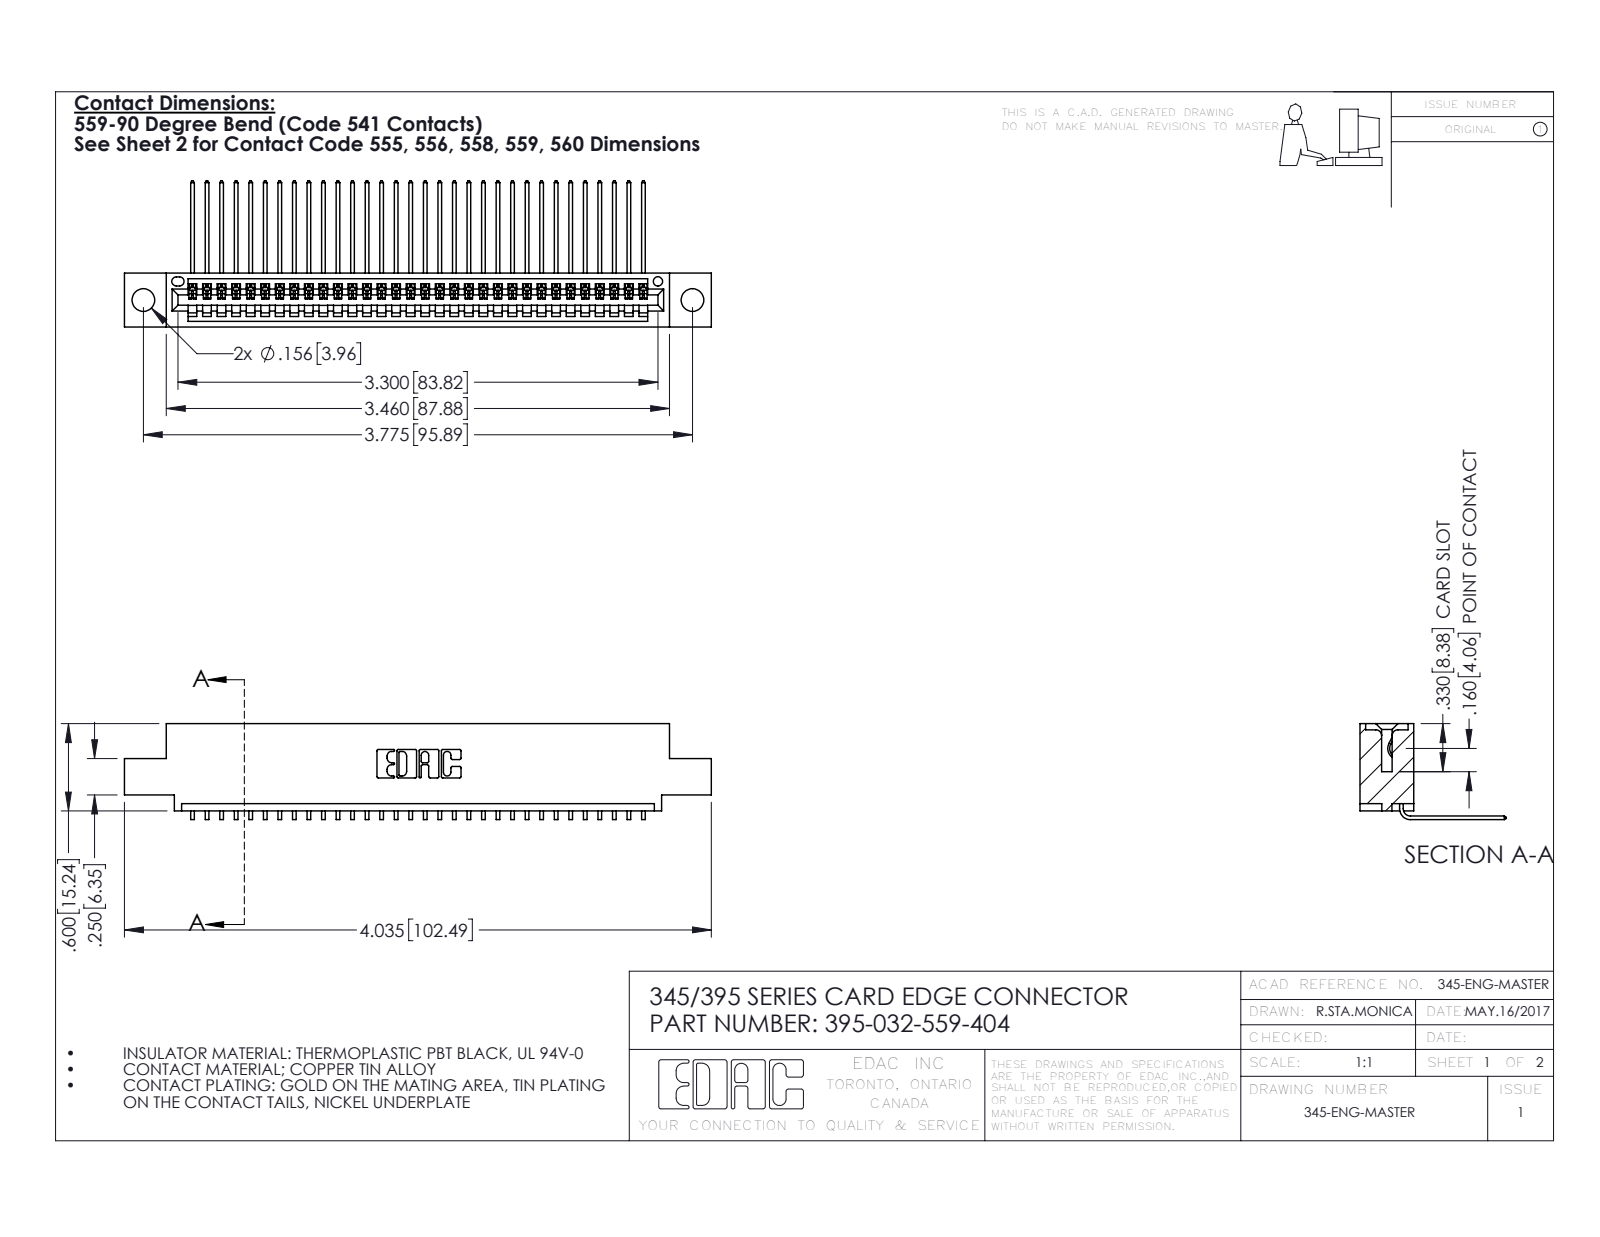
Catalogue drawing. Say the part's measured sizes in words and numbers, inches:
The part is named "395-032-559-404; 345 Part_0.110 Offset - 0.156 Dia-TH; 345-292-001_558 559 Tail - 1". Its 3-D file was written by "SolidWorks 2016 (CONFIG_CONTROL_DESIGN)". It is 33 solids with 2050 faces: 1428 planar, 622 cylindrical and 0 other. Overall it measures 4.035 by 1.005 by 0.659 inches. Its volume is 0.586 cubic inches and its surface area 20.36 square inches. Round holes: 2 of diameter 0.156, 1 of diameter 0.064. Partial cylindrical surfaces (rounded edges, fillets, slot ends): 64 of radius 0.006, 22 of radius 0.01, 6 of radius 0.007, 6 of radius 0.031, 3 of radius 0.026, 2 of radius 0.031, 2 of radius 0.04, 1 of radius 0.014. The main face-to-face distances are 0.072, 0.298, 0.37, 0.2, 0.098, 0.272, 0.025, 0.225, 0.149, 0.072. The hole center spacings are 0.27, 3.54, 3.775.
